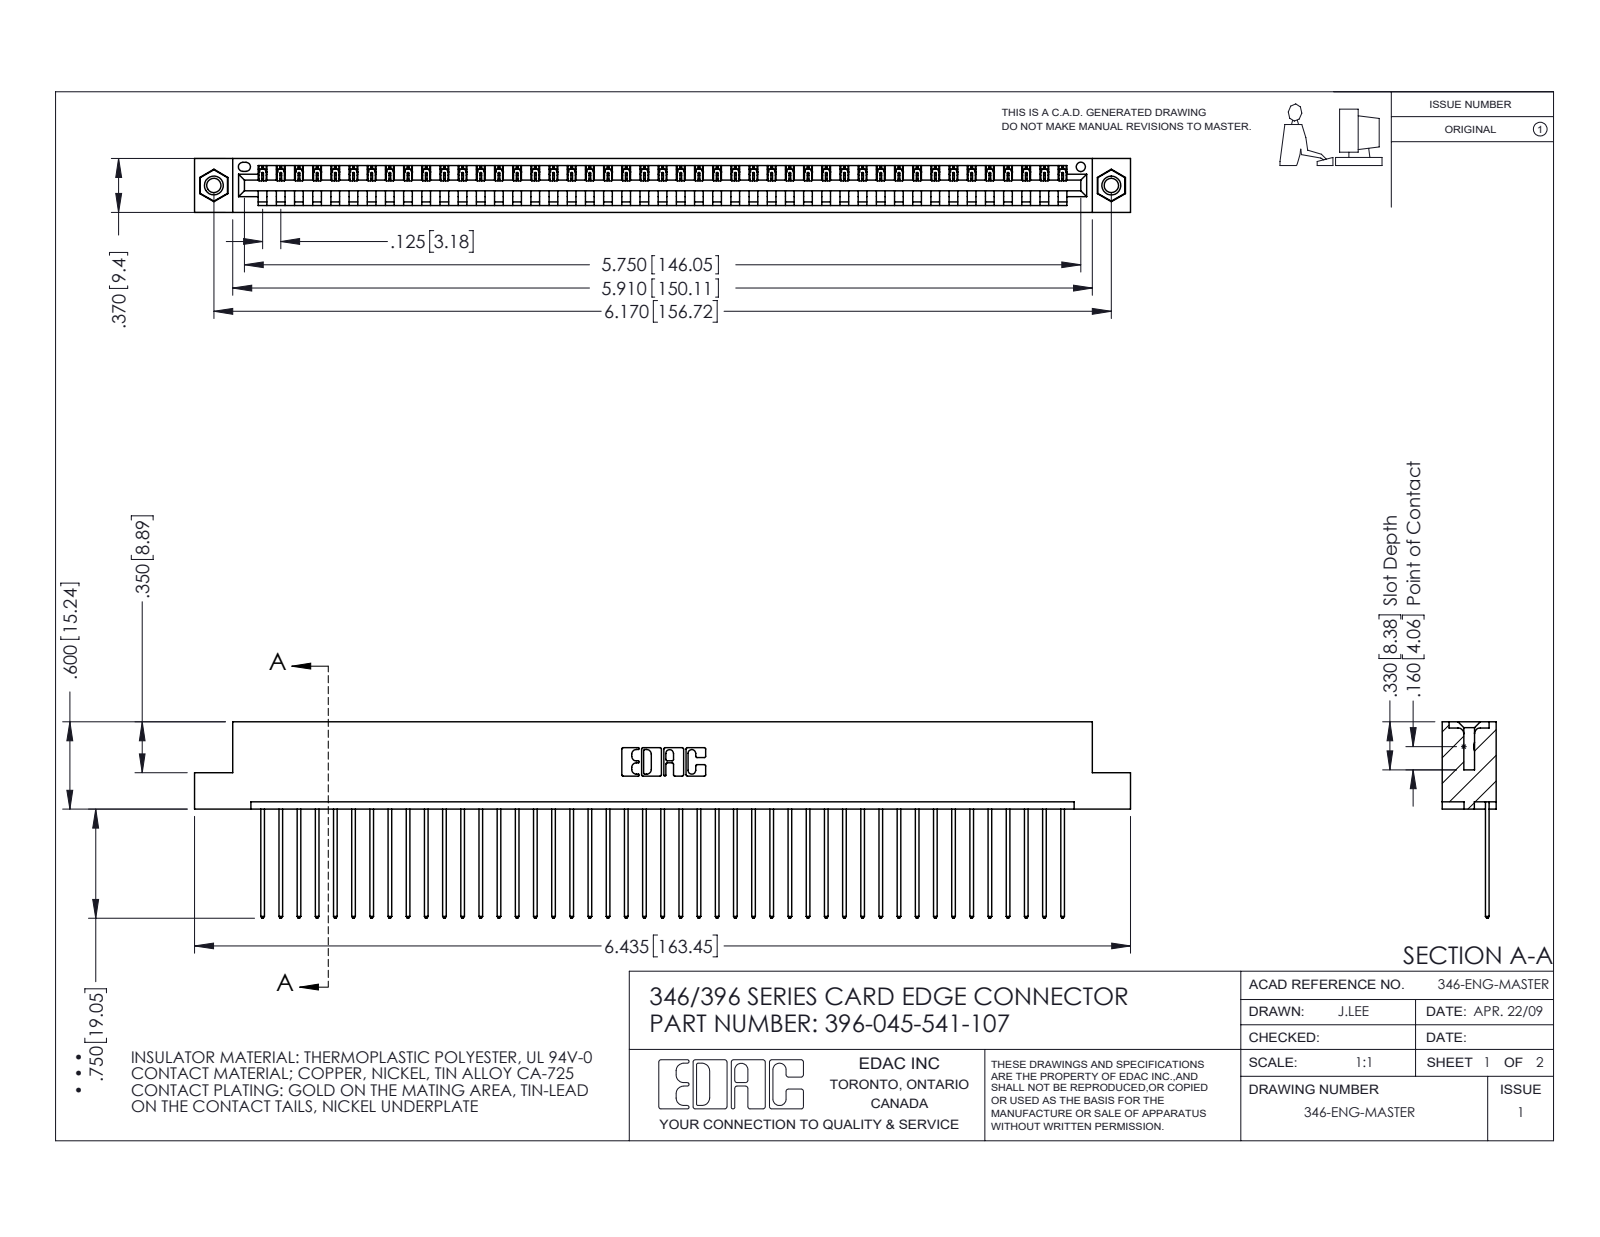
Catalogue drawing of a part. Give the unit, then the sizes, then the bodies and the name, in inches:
Units: inches
Overall size (bounding box): 6.435 × 1.35 × 0.37
Round holes (diameter × count): ⌀0.098 ×2, ⌀0.125 ×2, ⌀0.156 ×2, ⌀0.064 ×1
Round bosses / shafts (diameter × count): ⌀0.155 ×2
Partial cylindrical surfaces — rounded edges, fillets, slot ends (radius × count): R0.006 ×90, R0.01 ×90, R0.01 ×22, R0.007 ×6, R0.031 ×6, R0.026 ×3, R0.031 ×2, R0.04 ×2
Main face-to-face distances: 0.048, 0.322, 0.37, 0.25, 0.072, 0.298, 0.025, 0.148, 0.222, 0.1
Hole centre spacings: 0.246, 5.961, 6.17
Volume: 0.964 in³ · Surface area: 32.09 in²
Bodies: 48 solids, 2792 faces (1908 planar, 868 cylindrical, 16 other)
Part name (STEP PRODUCT): 396-045-541-107; 346 Part_Flush Mounting Lugs - 0.156 Dia-TI; 345-292-001_345-293-141; 345-250-001_345-250-005-103
STEP written by: SolidWorks 2016 (CONFIG_CONTROL_DESIGN)
